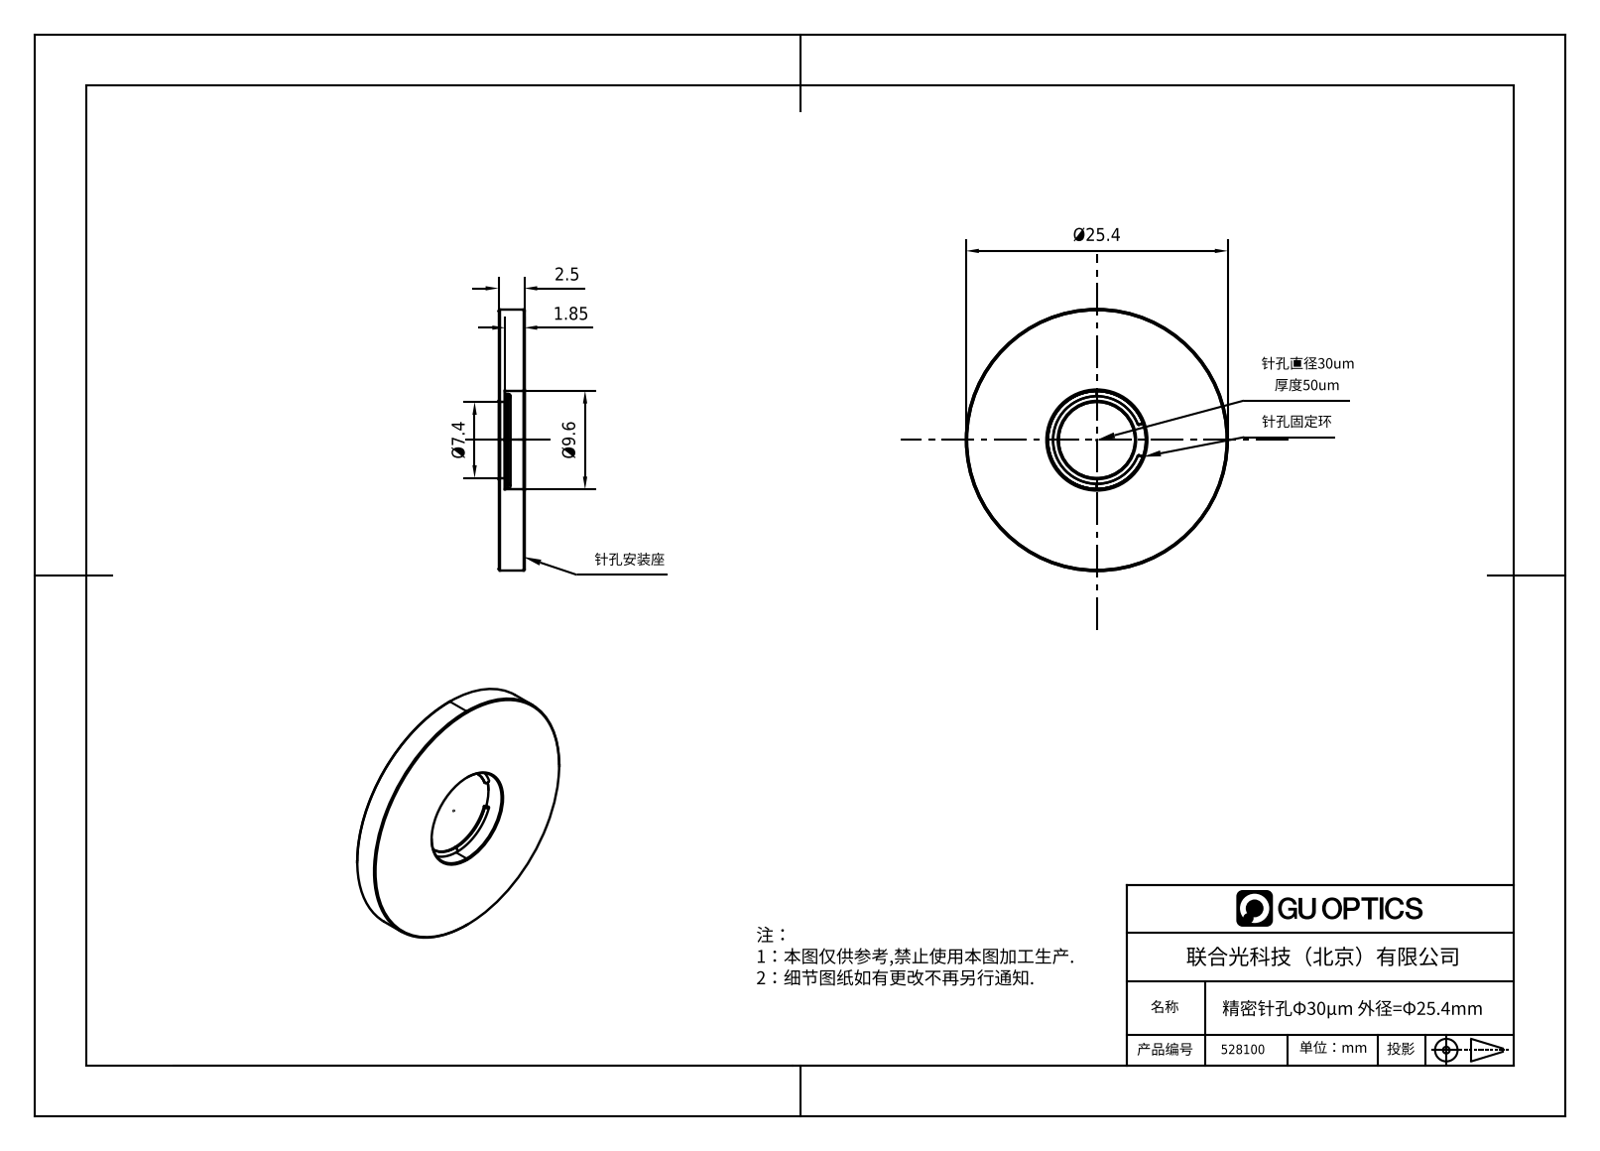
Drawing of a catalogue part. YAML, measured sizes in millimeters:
part_name: "1.5.3.26_ZXO-1.0-30_精密针孔30um，直径25.4（1.0英寸）"
step_written_by: "SolidWorks 2018 (CONFIG_CONTROL_DESIGN)"
units: millimeters
bodies: {solids: 0, faces: 26, planar: 6, cylindrical: 6, other: 14}
overall_size: [25.4, 25.4, 2.5]
round_holes:
  - {diameter: 7.4, count: 1}
  - {diameter: 9.6, count: 1}
round_bosses_or_shafts:
  - {diameter: 25.4, count: 1}
face_to_face_distances: [2.5, 0.6, 0.65, 1.9, 1.85]
